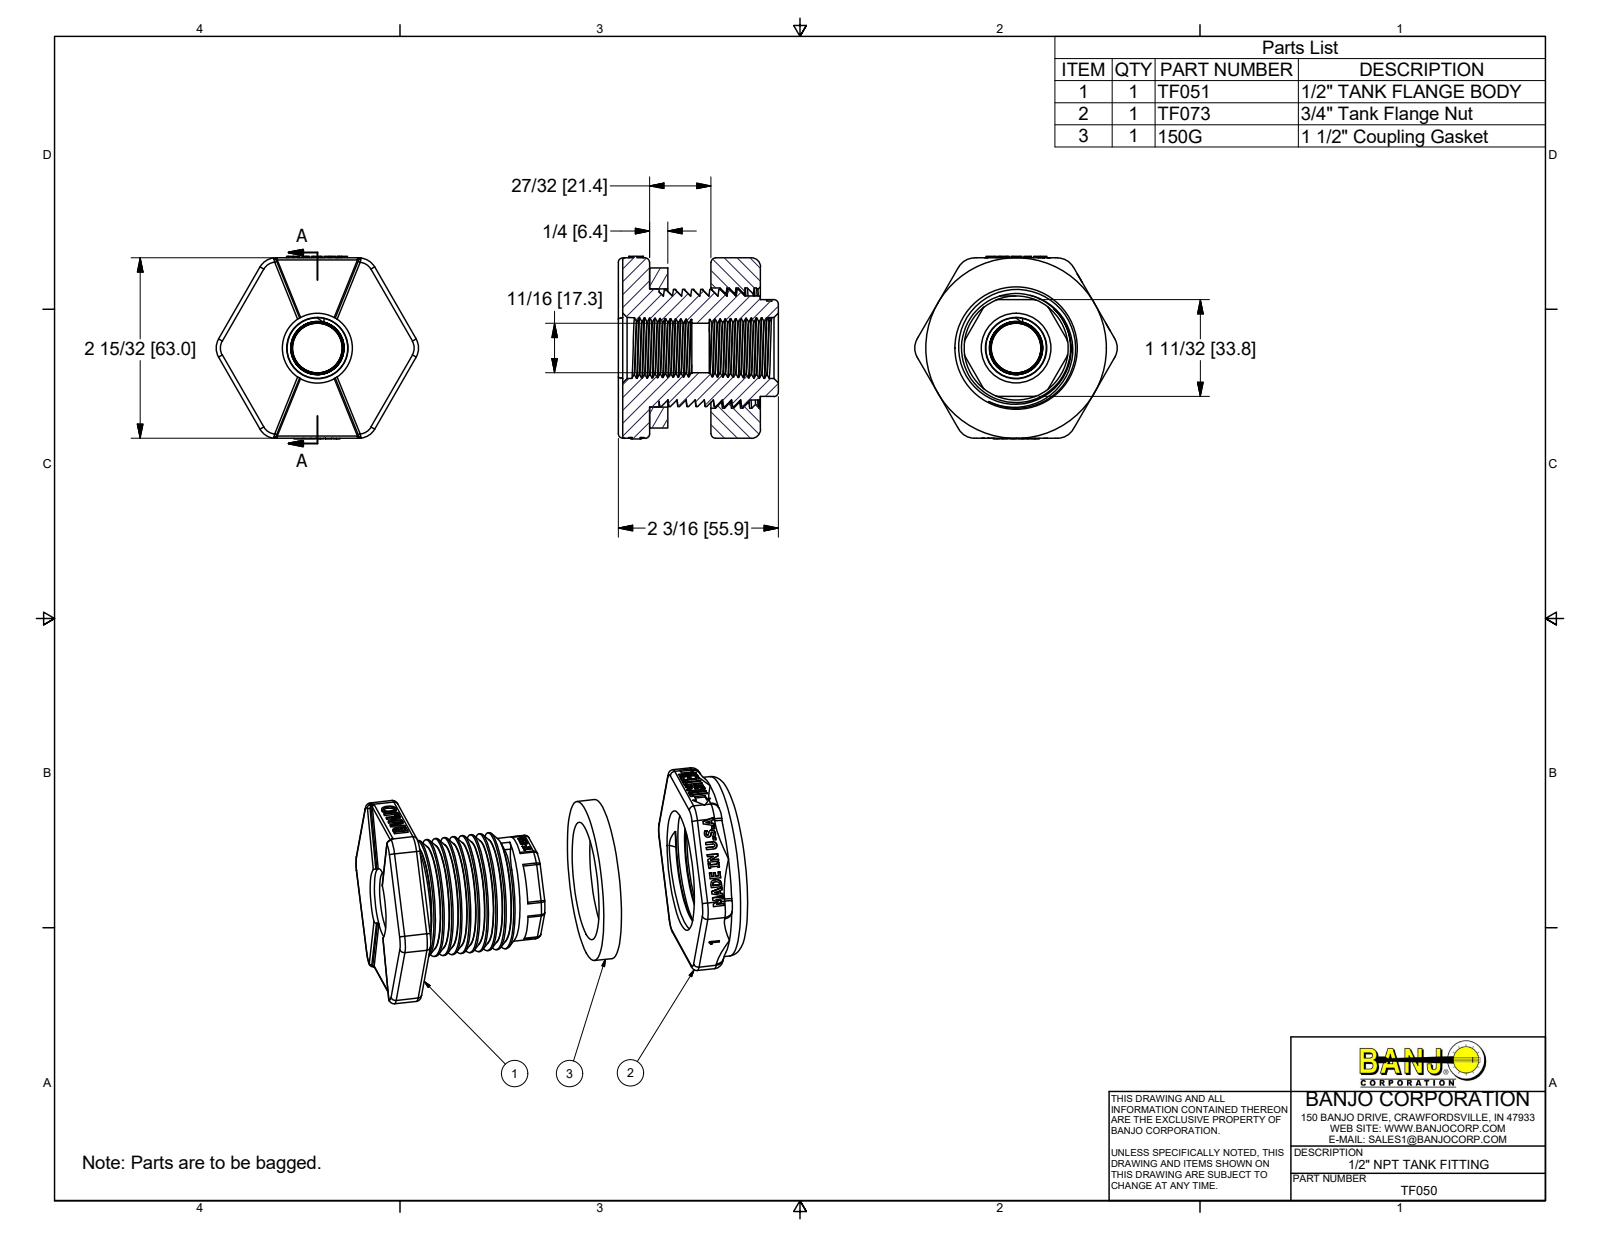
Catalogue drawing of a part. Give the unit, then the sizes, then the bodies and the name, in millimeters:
Units: millimetres
Overall size (bounding box): 70.77 × 63.75 × 55.88
Round holes (diameter × count): ⌀17.27 ×1, ⌀38.1 ×1, ⌀41.27 ×1, ⌀41.96 ×1
Round bosses / shafts (diameter × count): ⌀62.99 ×1, ⌀55.88 ×1, ⌀41.15 ×1, ⌀40.89 ×1, ⌀36.32 ×1
Partial cylindrical surfaces — rounded edges, fillets, slot ends (radius × count): R1.52 ×28, R0.76 ×6, R1.59 ×6, R3.17 ×6, R6.35 ×6, R0.38 ×4, R12.19 ×1, R12.42 ×1
Main face-to-face distances: 10.92, 32.35, 21.43, 6.35, 17.27, 15.08, 32.36, 49.63, 38.71, 17.28
Volume: 111 756 mm³ · Surface area: 37 601 mm²
Bodies: 3 solids, 891 faces (501 planar, 95 cylindrical, 295 other)
Part name (STEP PRODUCT): TF050U; TF051; TF073; TF073X (+1 more)
STEP written by: Autodesk Inventor 2017 (AUTOMOTIVE_DESIGN)
